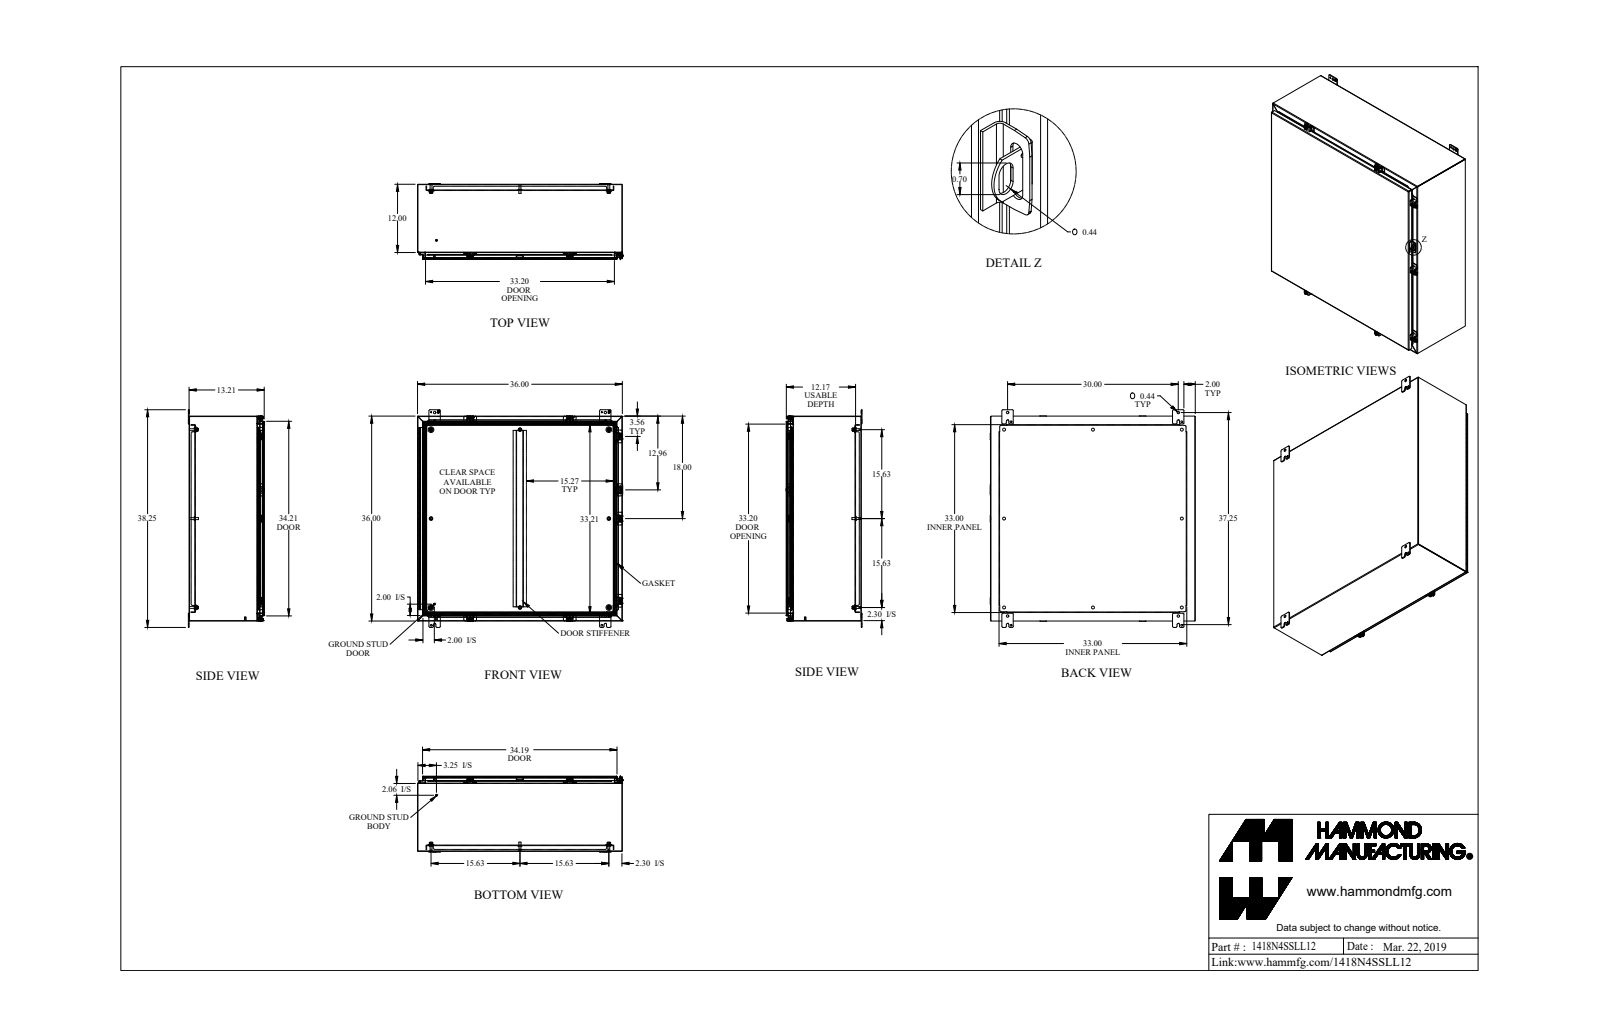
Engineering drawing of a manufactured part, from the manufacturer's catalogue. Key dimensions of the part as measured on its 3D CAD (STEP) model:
Part name (STEP PRODUCT): 1418N4SSLL12_Default
STEP written by: SolidWorks 2019 (CONFIG_CONTROL_DESIGN)
Units: inches
Bodies: 62 solids, 2137 faces (1291 planar, 732 cylindrical, 114 other)
Overall size (bounding box): 38.25 × 36.063 × 13.375
Volume: 475.9 in³ · Surface area: 12 466 in²
Round holes (diameter × count): ⌀0.5 ×8, ⌀0.213 ×7, ⌀0.265 ×7, ⌀0.375 ×7, ⌀0.307 ×4, ⌀0.313 ×4, ⌀0.437 ×4, ⌀0.445 ×4, ⌀0.125 ×1, ⌀0.187 ×1
Round bosses / shafts (diameter × count): ⌀0.65 ×8, ⌀0.375 ×8, ⌀0.332 ×8, ⌀0.5 ×7, ⌀0.39 ×7, ⌀0.244 ×7, ⌀1 ×4, ⌀0.313 ×2
Partial cylindrical surfaces — rounded edges, fillets, slot ends (radius × count): R0.25 ×40, R0.048 ×33, R0.143 ×33, R0.188 ×30, R0.036 ×22, R0.108 ×22, R0.141 ×14, R0.125 ×12
Main face-to-face distances: 0.072, 35.928, 13.066, 13.138, 0.072, 13.138, 0.095, 13.21, 0.937, 1.009
Hole centre spacings: 15.625, 31.25, 34.939, 7.196, 9.004, 15.625, 19.035, 24.468
